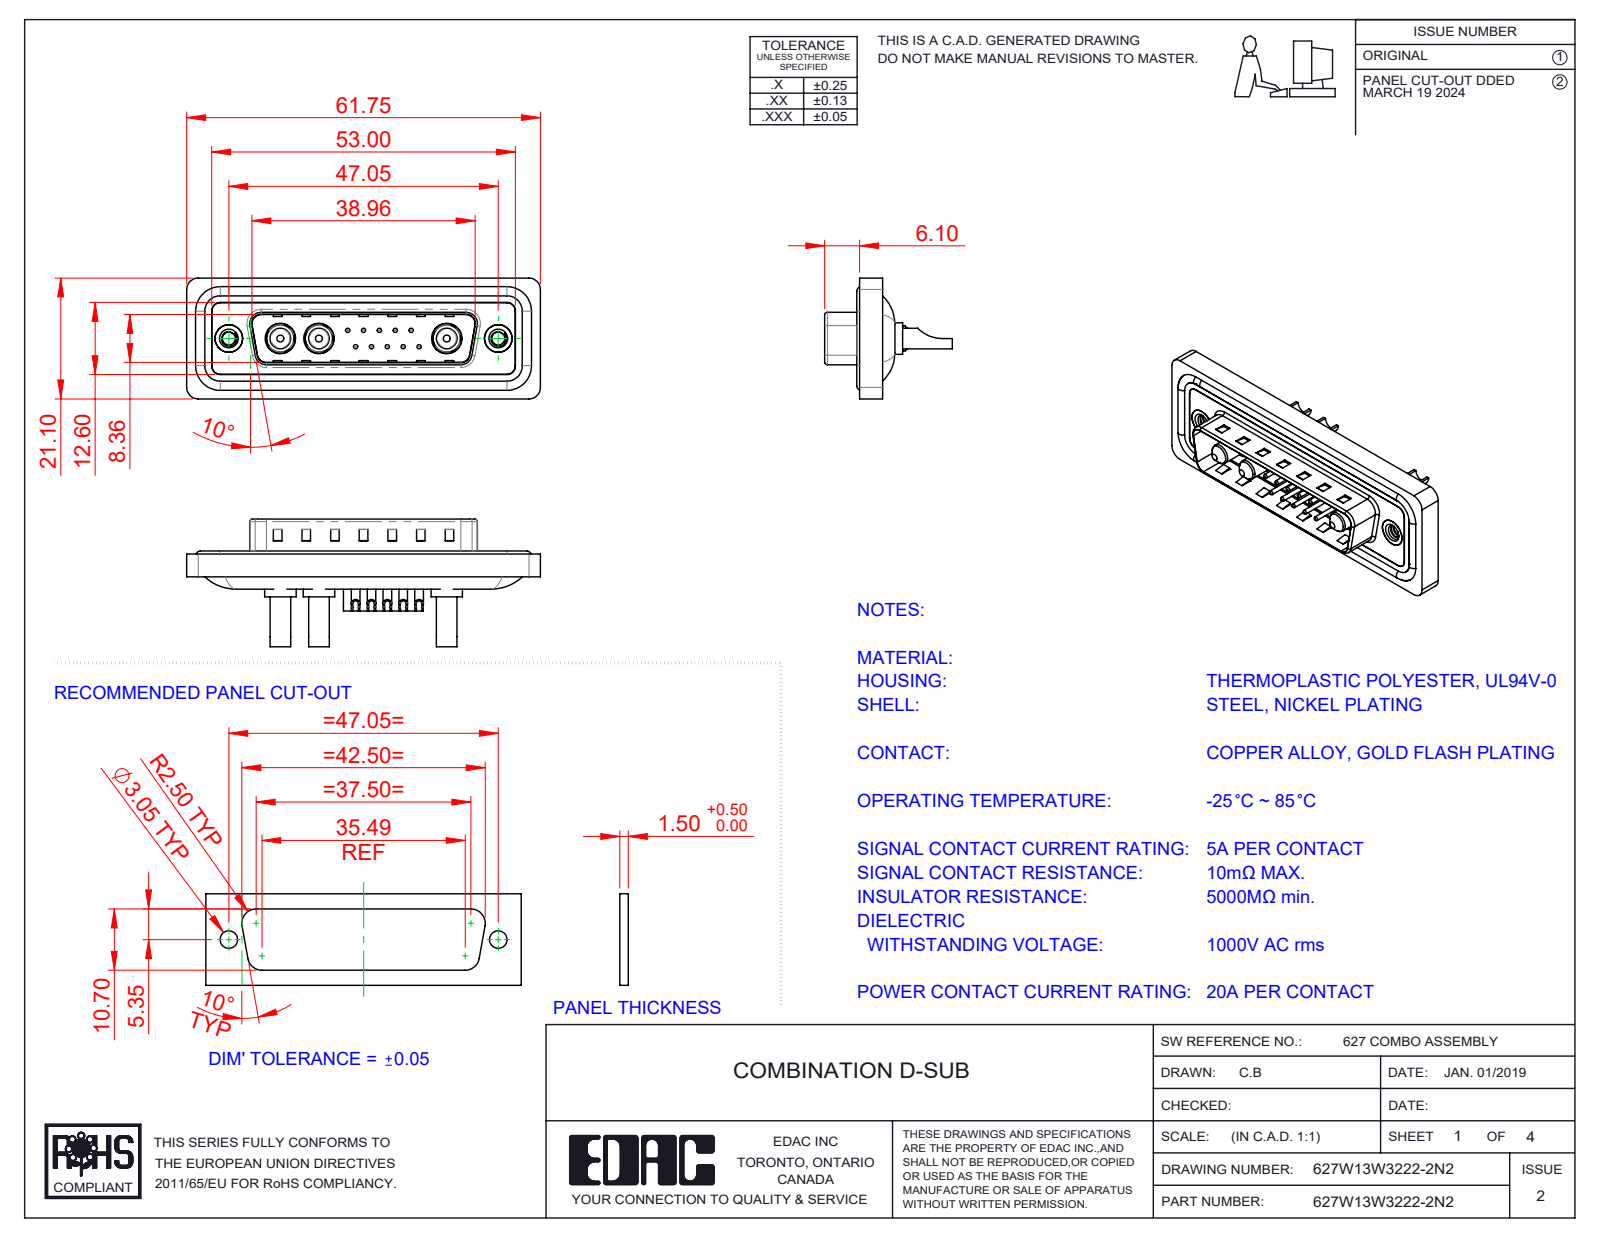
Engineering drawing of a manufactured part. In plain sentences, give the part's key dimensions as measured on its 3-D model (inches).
The part is named "627Combo Contact Row 1_22; 627Combo Threaded Rivet_2; Power Pin_20A SC; 627Combo Housing_13W3 (+5 more)". Its 3-D file was written by "SolidWorks 2023 (CONFIG_CONTROL_DESIGN)". It is 23 solids with 991 faces: 338 planar, 414 cylindrical and 239 other. Overall it measures 2.431 by 0.878 by 0.831 inches. Its volume is 0.451 cubic inches and its surface area 18.91 square inches. Round holes: 10 of diameter 0.03, 10 of diameter 0.039, 10 of diameter 0.063, 10 of diameter 0.079, 3 of diameter 0.106, 3 of diameter 0.191, 3 of diameter 0.209, 2 of diameter 0.089, 2 of diameter 0.157, 2 of diameter 0.189, 2 of diameter 0.197. Round bosses or shafts: 10 of diameter 0.059, 4 of diameter 0.063, 3 of diameter 0.217, 3 of diameter 0.205, 3 of diameter 0.187, 3 of diameter 0.148, 3 of diameter 0.142, 2 of diameter 0.193. Partial cylindrical surfaces (rounded edges, fillets, slot ends): 22 of radius 0.059, 18 of radius 0.079, 8 of radius 0.02, 8 of radius 0.063, 6 of radius 0.039, 4 of radius 0.01, 4 of radius 0.024, 4 of radius 0.026. The main face-to-face distances are 0.016, 0.059, 0.043, 0.063, 0.02, 0.122, 0.114, 0.032, 0.377, 0.161. The hole center spacings are 0.124, 0.109, 0.198, 0.218, 0.295, 0.198, 0.327, 0.398.
